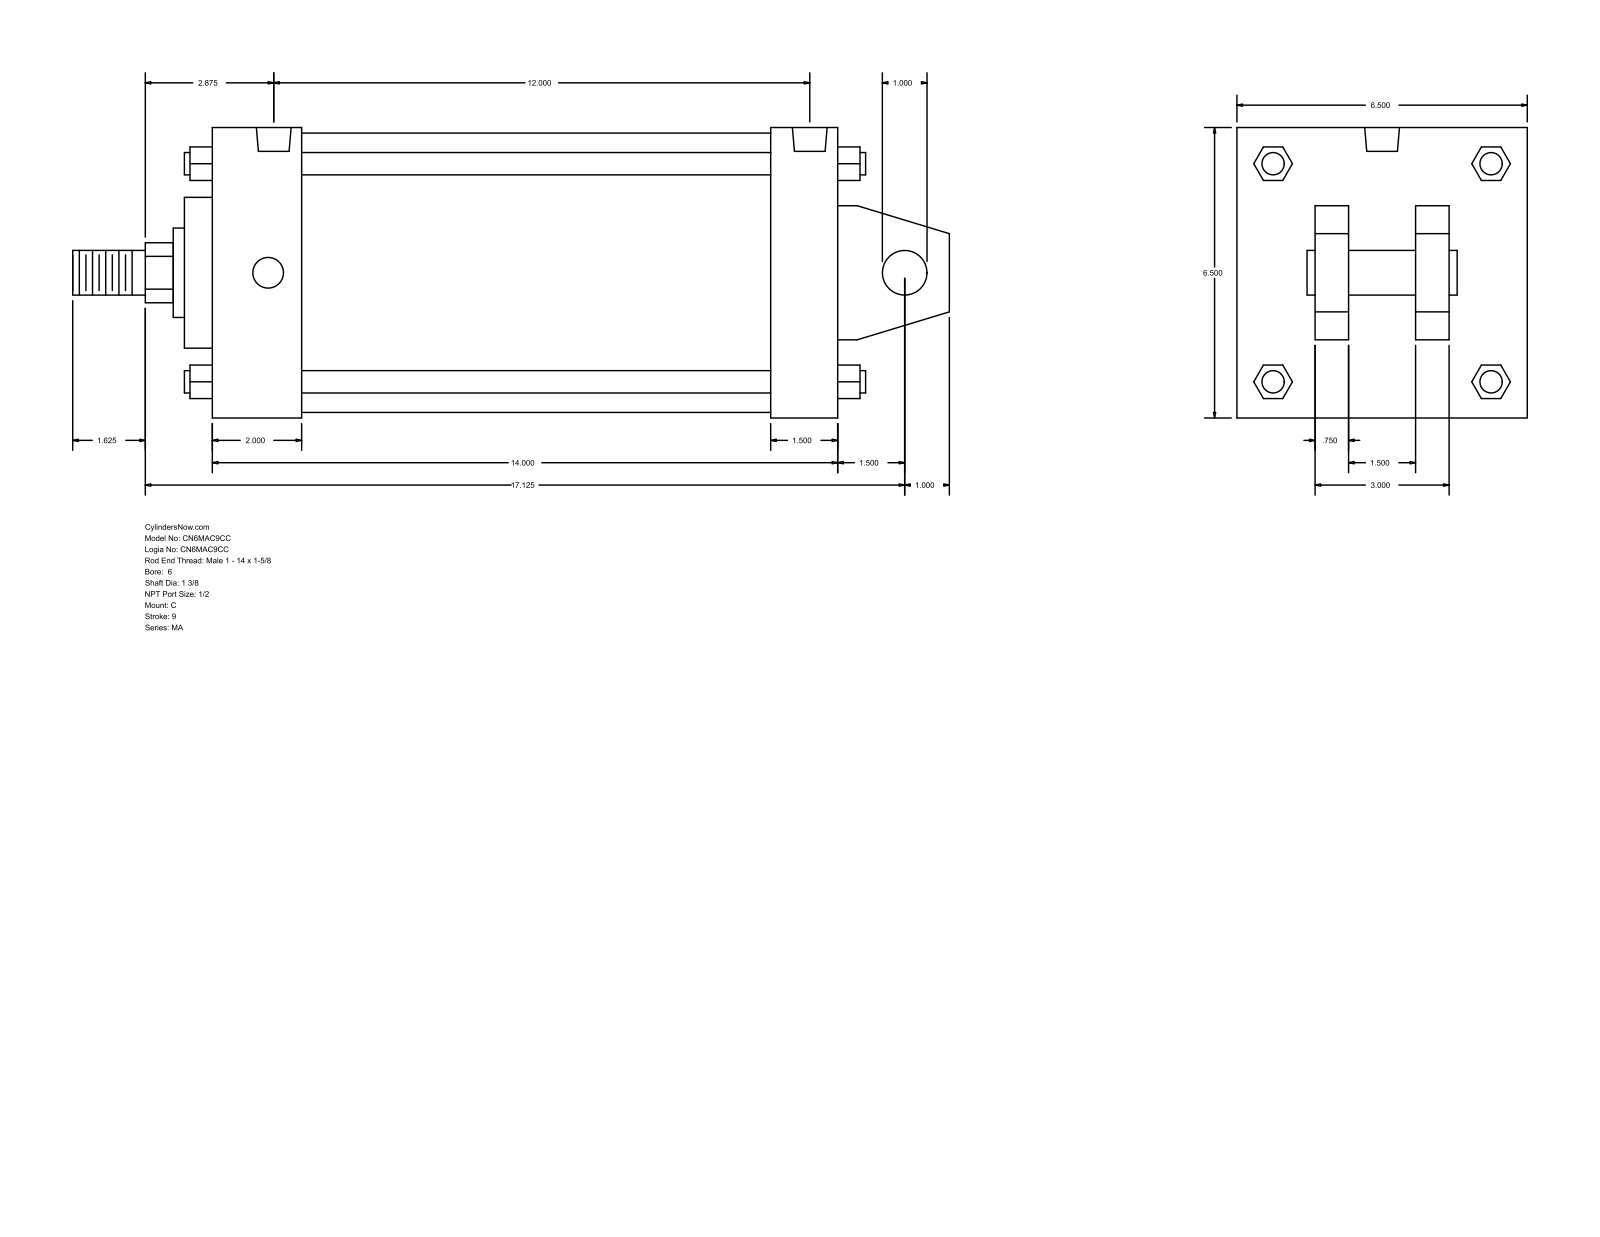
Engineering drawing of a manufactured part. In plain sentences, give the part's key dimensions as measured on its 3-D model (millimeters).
The part is named "MA_C__0600_1.375". Its 3-D file was written by "GSSL Pune (CONFIG_CONTROL_DESIGN)". It is 0 solids with 141 faces: 109 planar, 32 cylindrical and 0 other. Overall it measures 498.48 by 165.1 by 165.1 millimeters. Round holes: 4 of diameter 17.46, 2 of diameter 19.77. Round bosses or shafts: 4 of diameter 12.7, 2 of diameter 25.4, 1 of diameter 158.75, 1 of diameter 85.72, 1 of diameter 50.8, 1 of diameter 34.92. Partial cylindrical surfaces (rounded edges, fillets, slot ends): 1 of radius 17.06. The main face-to-face distances are 165.1, 355.6, 38.1, 19.05, 63.5, 101.6, 50.8, 120.65, 44.45, 317.5. The hole center spacings are 304.8, 3.17, 3.18, 301.62, 304.79, 307.97.
